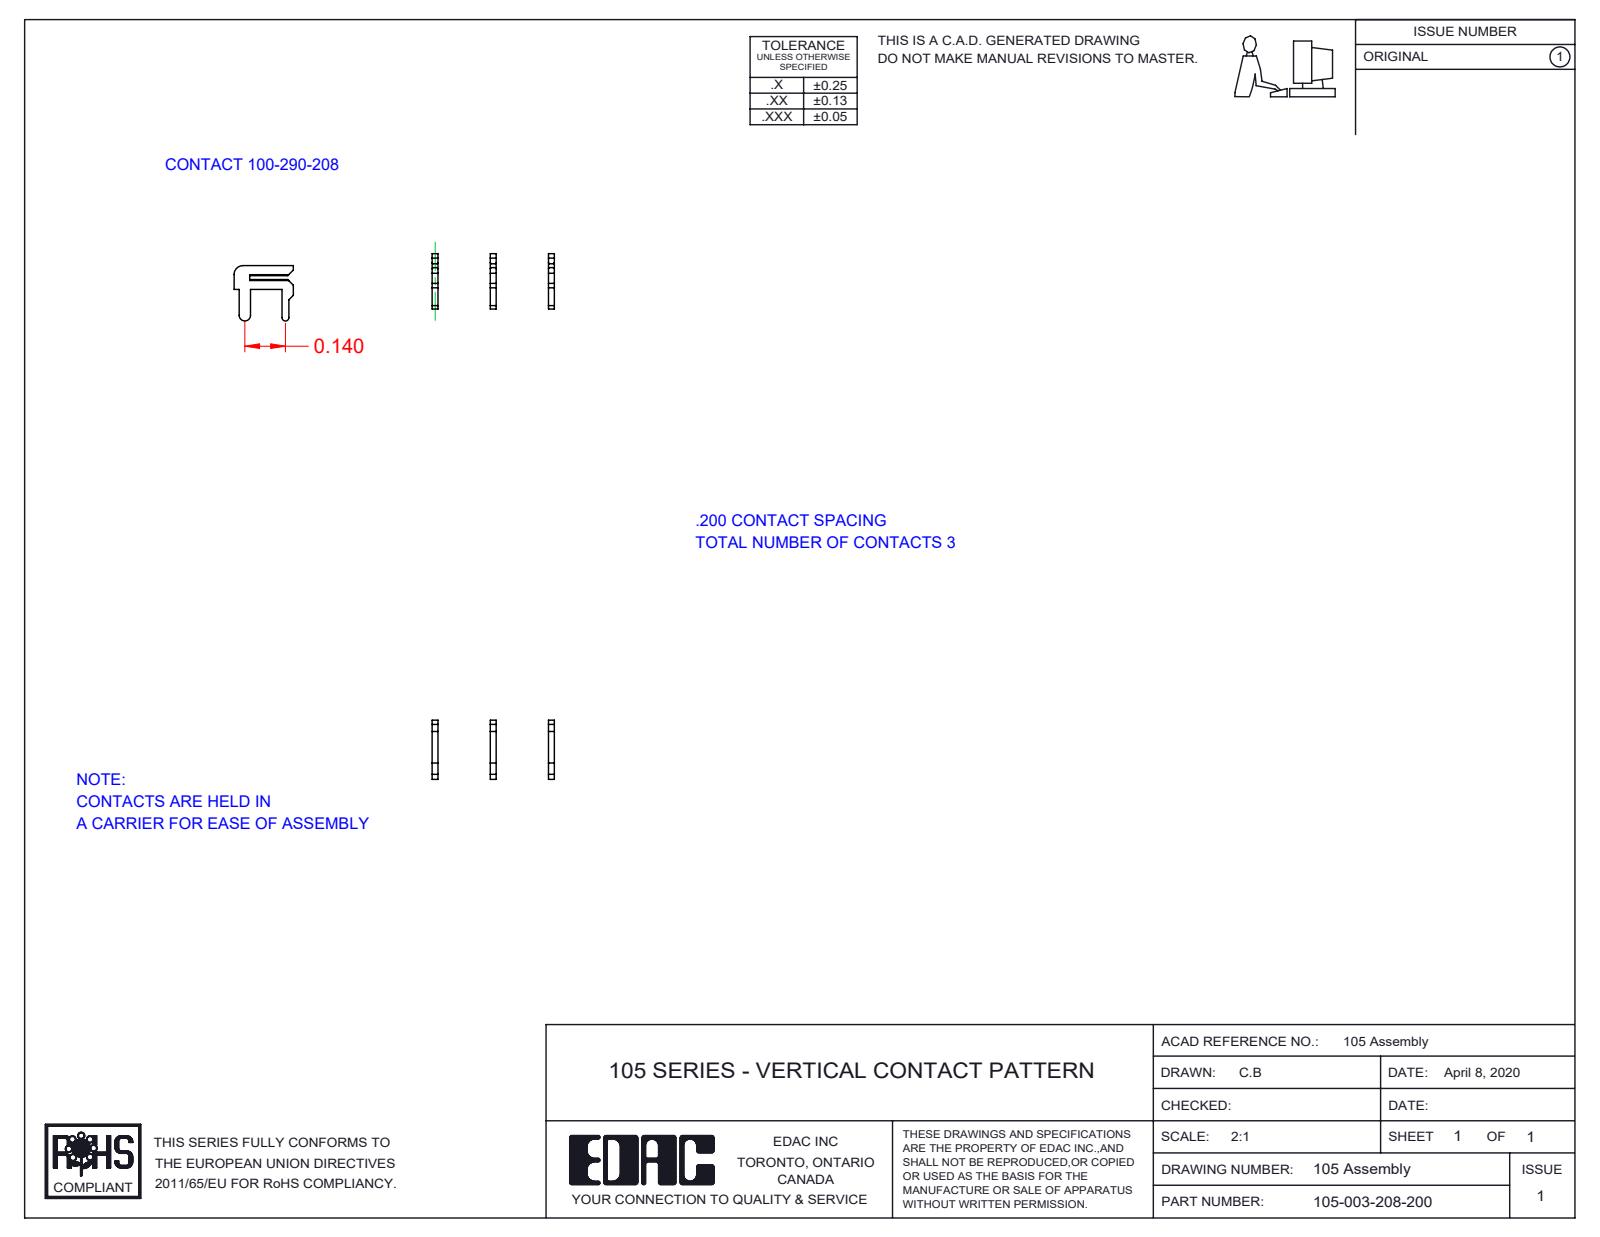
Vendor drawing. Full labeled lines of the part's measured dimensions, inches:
Part name (STEP PRODUCT): 105-003-208-200; 100-290-001_100-290-208
STEP written by: SolidWorks 2016 (CONFIG_CONTROL_DESIGN)
Units: inches
Bodies: 3 solids, 75 faces (66 planar, 9 cylindrical, 0 other)
Overall size (bounding box): 0.42 × 0.204 × 0.19
Volume: 0.001 in³ · Surface area: 0.198 in²
Partial cylindrical surfaces — rounded edges, fillets, slot ends (radius × count): R0.012 ×1, R0.019 ×1, R0.03 ×1
Main face-to-face distances: 0.2, 0.02, 0.4, 0.22, 0.18, 0.42, 0.38, 0.034, 0.048, 0.147
